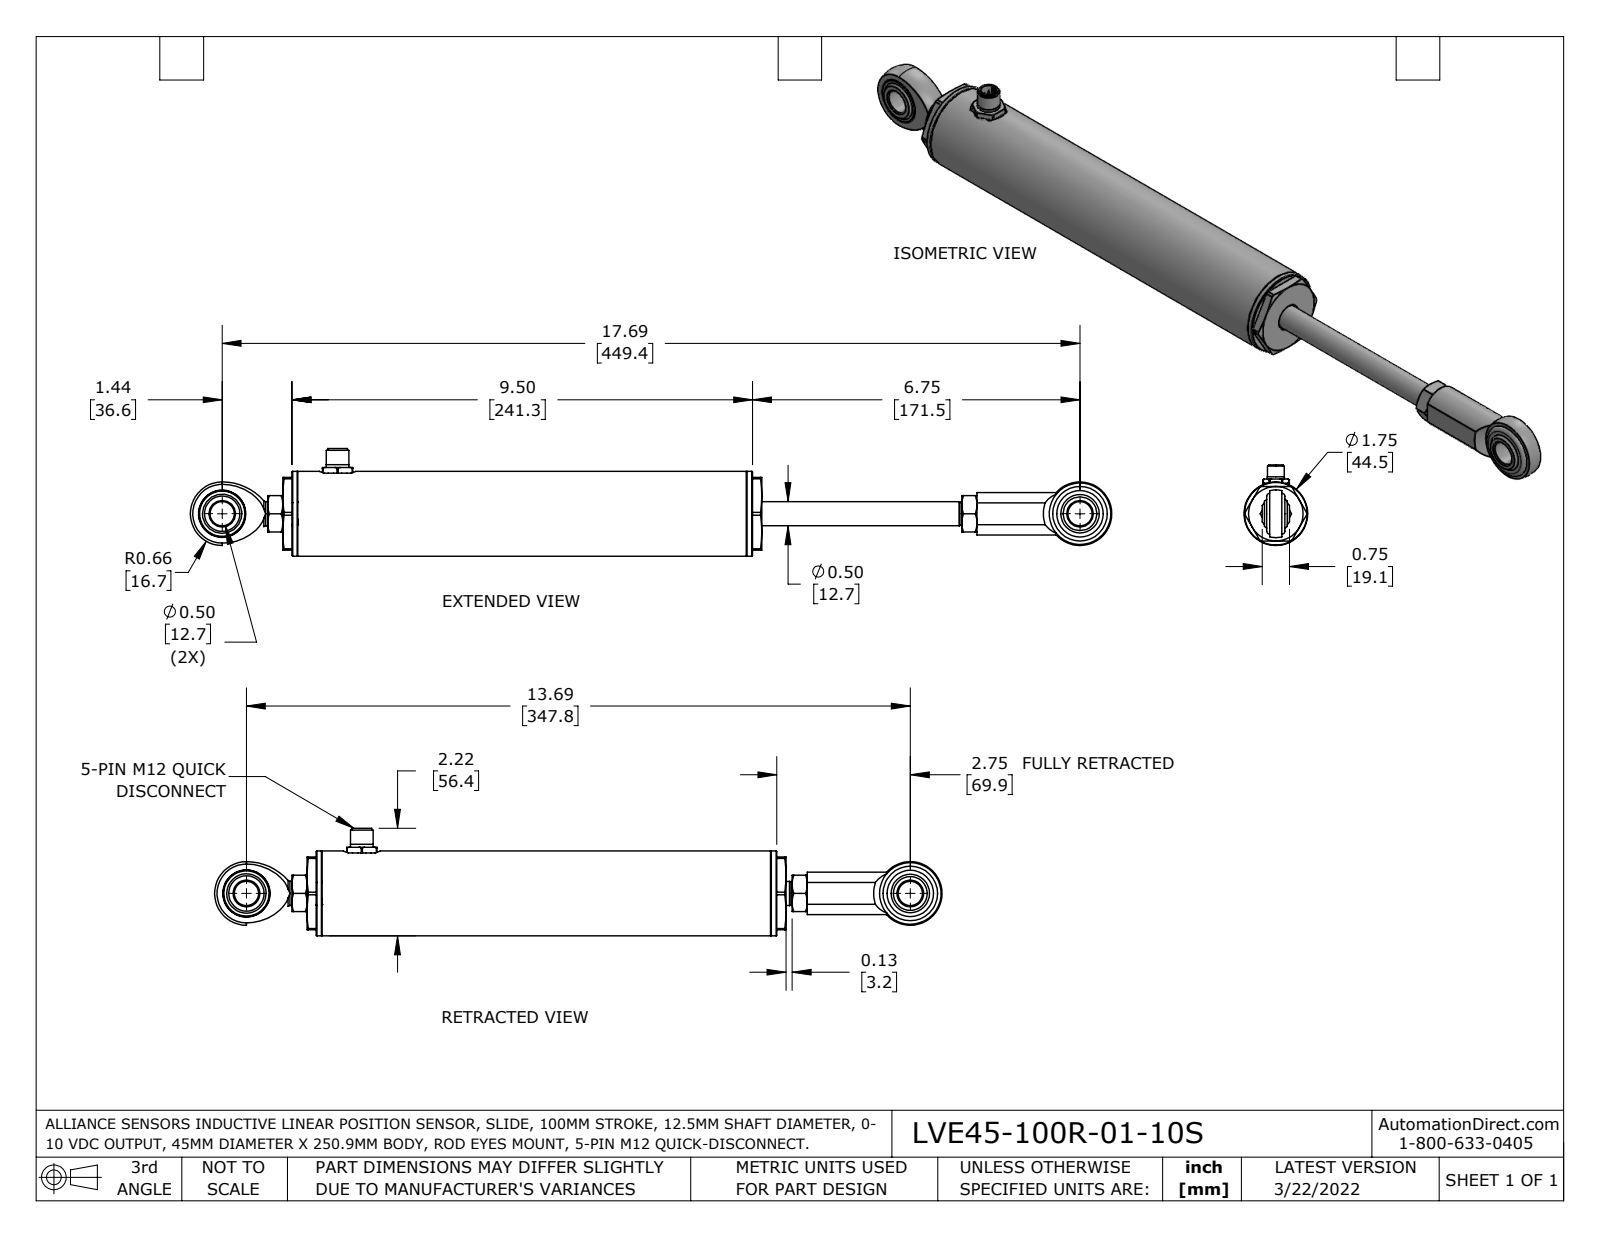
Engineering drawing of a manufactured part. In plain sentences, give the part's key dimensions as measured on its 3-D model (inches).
The part is named "3100-0041-XX-Z_3100-0041-04-Z; LVE45-100R-01-10S; 3100-0020; 3100-0013 (+8 more)". Its 3-D file was written by "SolidWorks 2021 (AUTOMOTIVE_DESIGN)". It is 23 solids with 873 faces: 198 planar, 297 cylindrical and 378 other. Overall it measures 19.004 by 2.219 by 1.75 inches. Its volume is 14.18 cubic inches and its surface area 201.9 square inches. Round holes: 3 of diameter 0.501, 1 of diameter 0.197, 1 of diameter 0.25, 1 of diameter 0.264, 1 of diameter 0.309, 1 of diameter 0.329, 1 of diameter 0.339, 1 of diameter 0.413, 1 of diameter 0.417, 1 of diameter 0.453, 1 of diameter 0.478, 1 of diameter 0.5. Round bosses or shafts: 5 of diameter 0.031, 1 of diameter 1.75, 1 of diameter 1.625, 1 of diameter 1.562, 1 of diameter 1.531, 1 of diameter 1.5, 1 of diameter 1.47, 1 of diameter 1.384. Partial cylindrical surfaces (rounded edges, fillets, slot ends): 1 of radius 0.325, 1 of radius 0.354, 1 of radius 0.378, 1 of radius 0.38, 1 of radius 0.438, 1 of radius 0.85. The main face-to-face distances are 1.93, 0.5, 0.38, 0.69, 2.62, 7.573, 2.24, 1.55, 7.763, 7.073. The hole center spacings are 0.5, 17.693.
